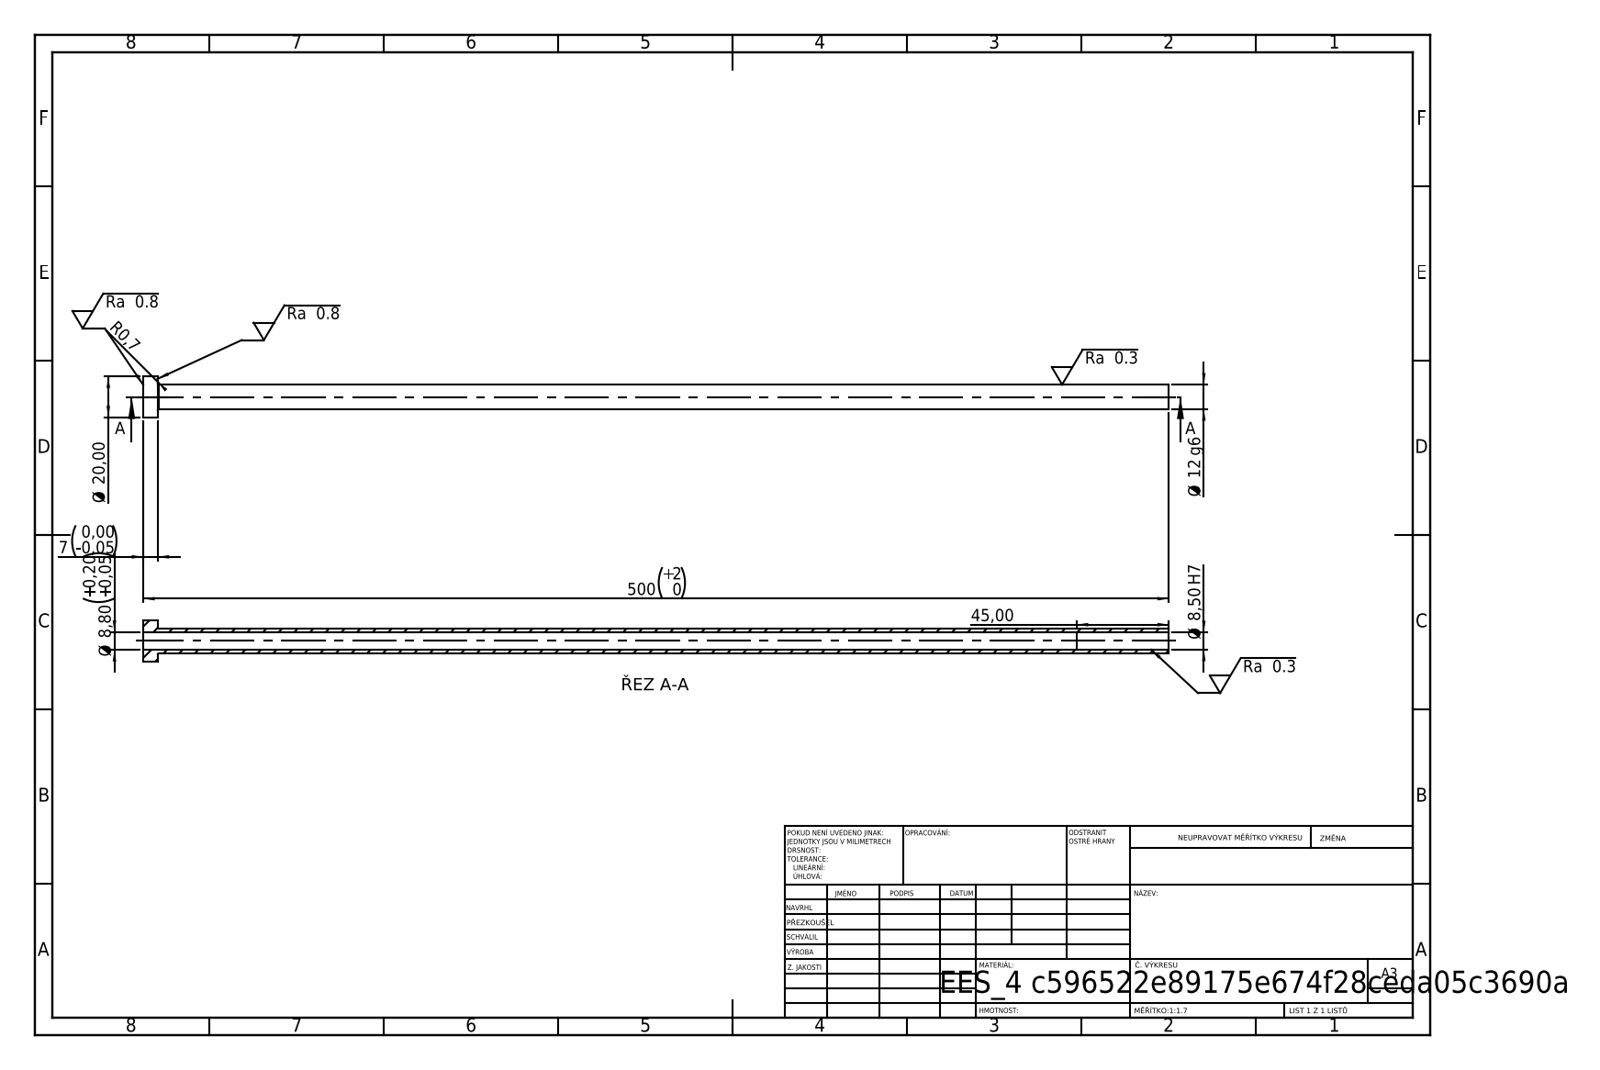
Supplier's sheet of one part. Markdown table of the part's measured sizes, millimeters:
| quantity | value |
| --- | --- |
| STEP written by | SolidWorks 2019 (CONFIG_CONTROL_DESIGN) |
| units | millimeters |
| bodies | 1 solid, 14 faces (4 planar, 8 cylindrical, 2 other) |
| overall size | 500 × 20 × 20 |
| volume | 27 733 mm³ |
| surface area | 33 310 mm² |
| round holes (diameter × count) | 8.5 × 1, 8.8 × 1 |
| round bosses / shafts (diameter × count) | 20 × 1, 12 × 1 |
| main face-to-face distances | 7, 500, 493, 455, 448, 45 |
